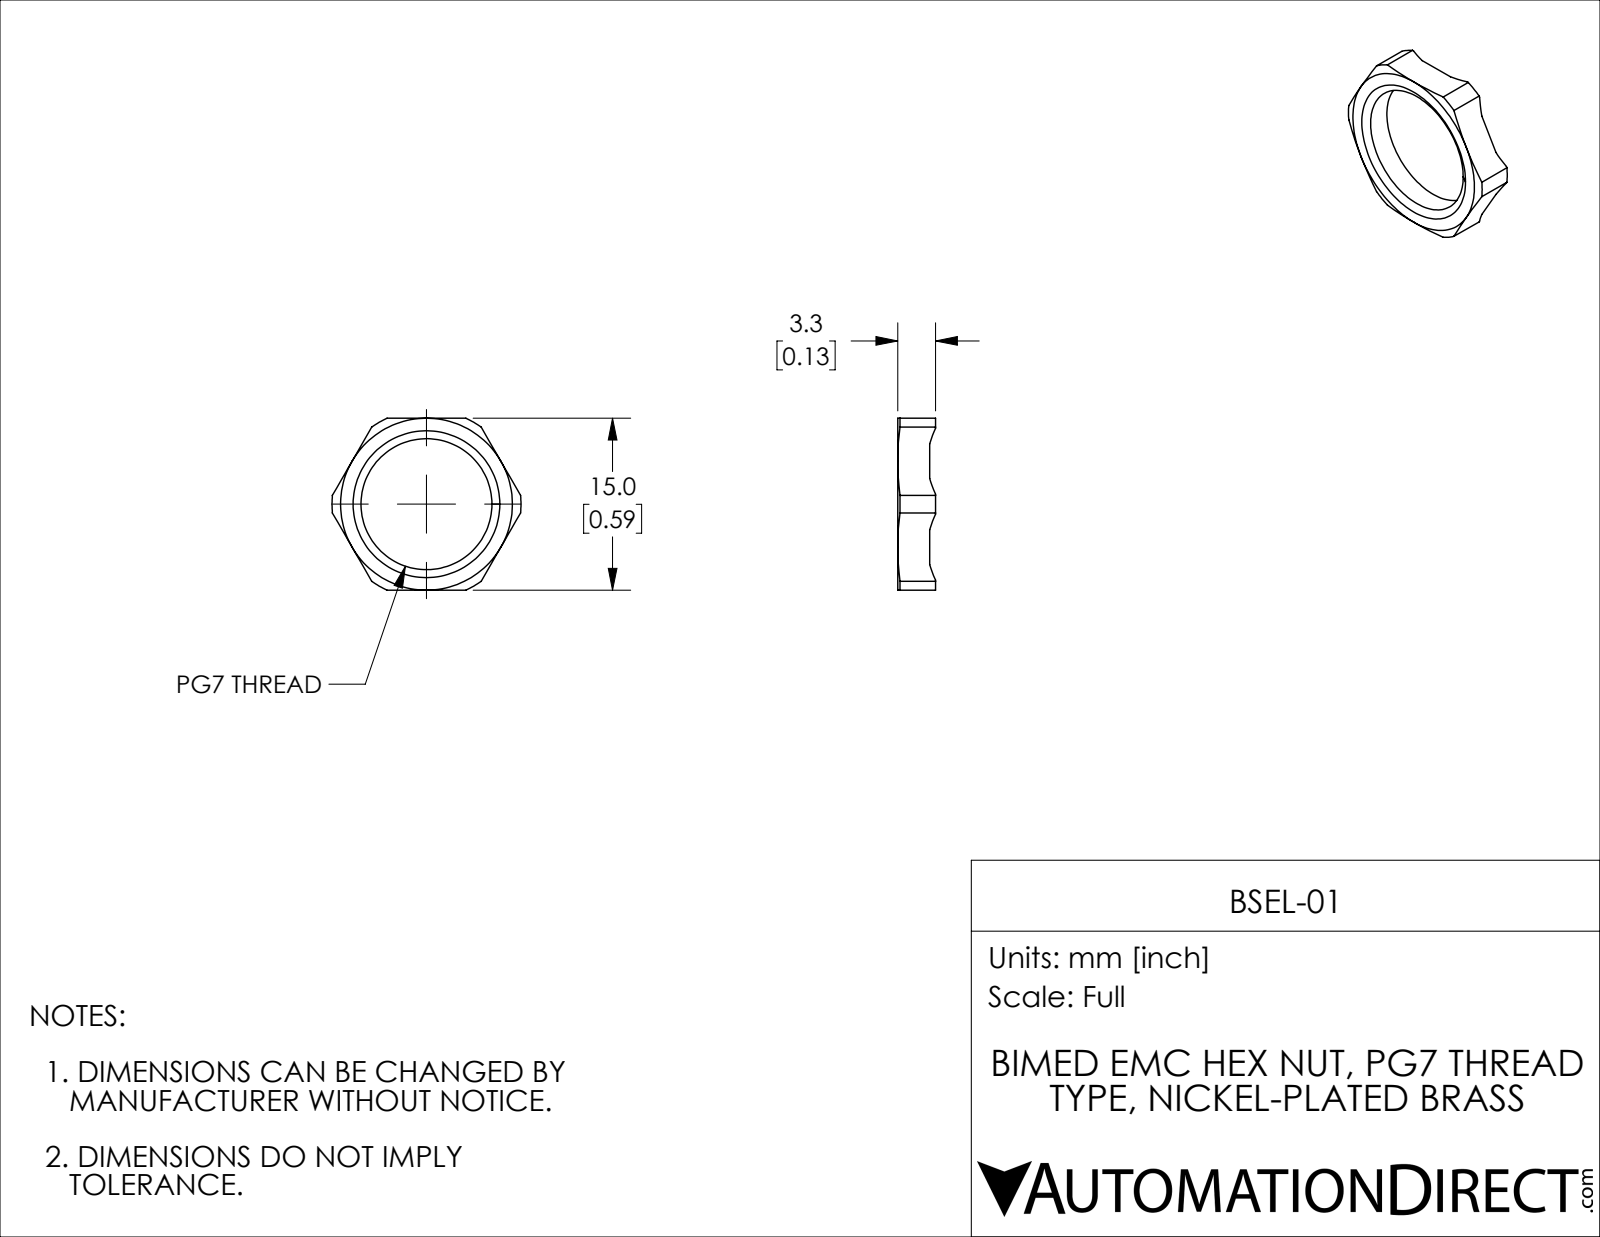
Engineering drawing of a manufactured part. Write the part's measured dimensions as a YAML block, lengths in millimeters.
part_name: "BSEL-01"
step_written_by: "SolidWorks 2021 (CONFIG_CONTROL_DESIGN)"
units: millimeters
bodies: {solids: 1, faces: 46, planar: 14, cylindrical: 8, other: 24}
overall_size: [16.5, 15, 3.3]
volume: 244
surface_area: 412
round_holes:
  - {diameter: 11.43, count: 1}
partial_cylinders:
  - {radius: 8.25, count: 1}
face_to_face_distances: [15, 2.8, 0.5, 3.3]
